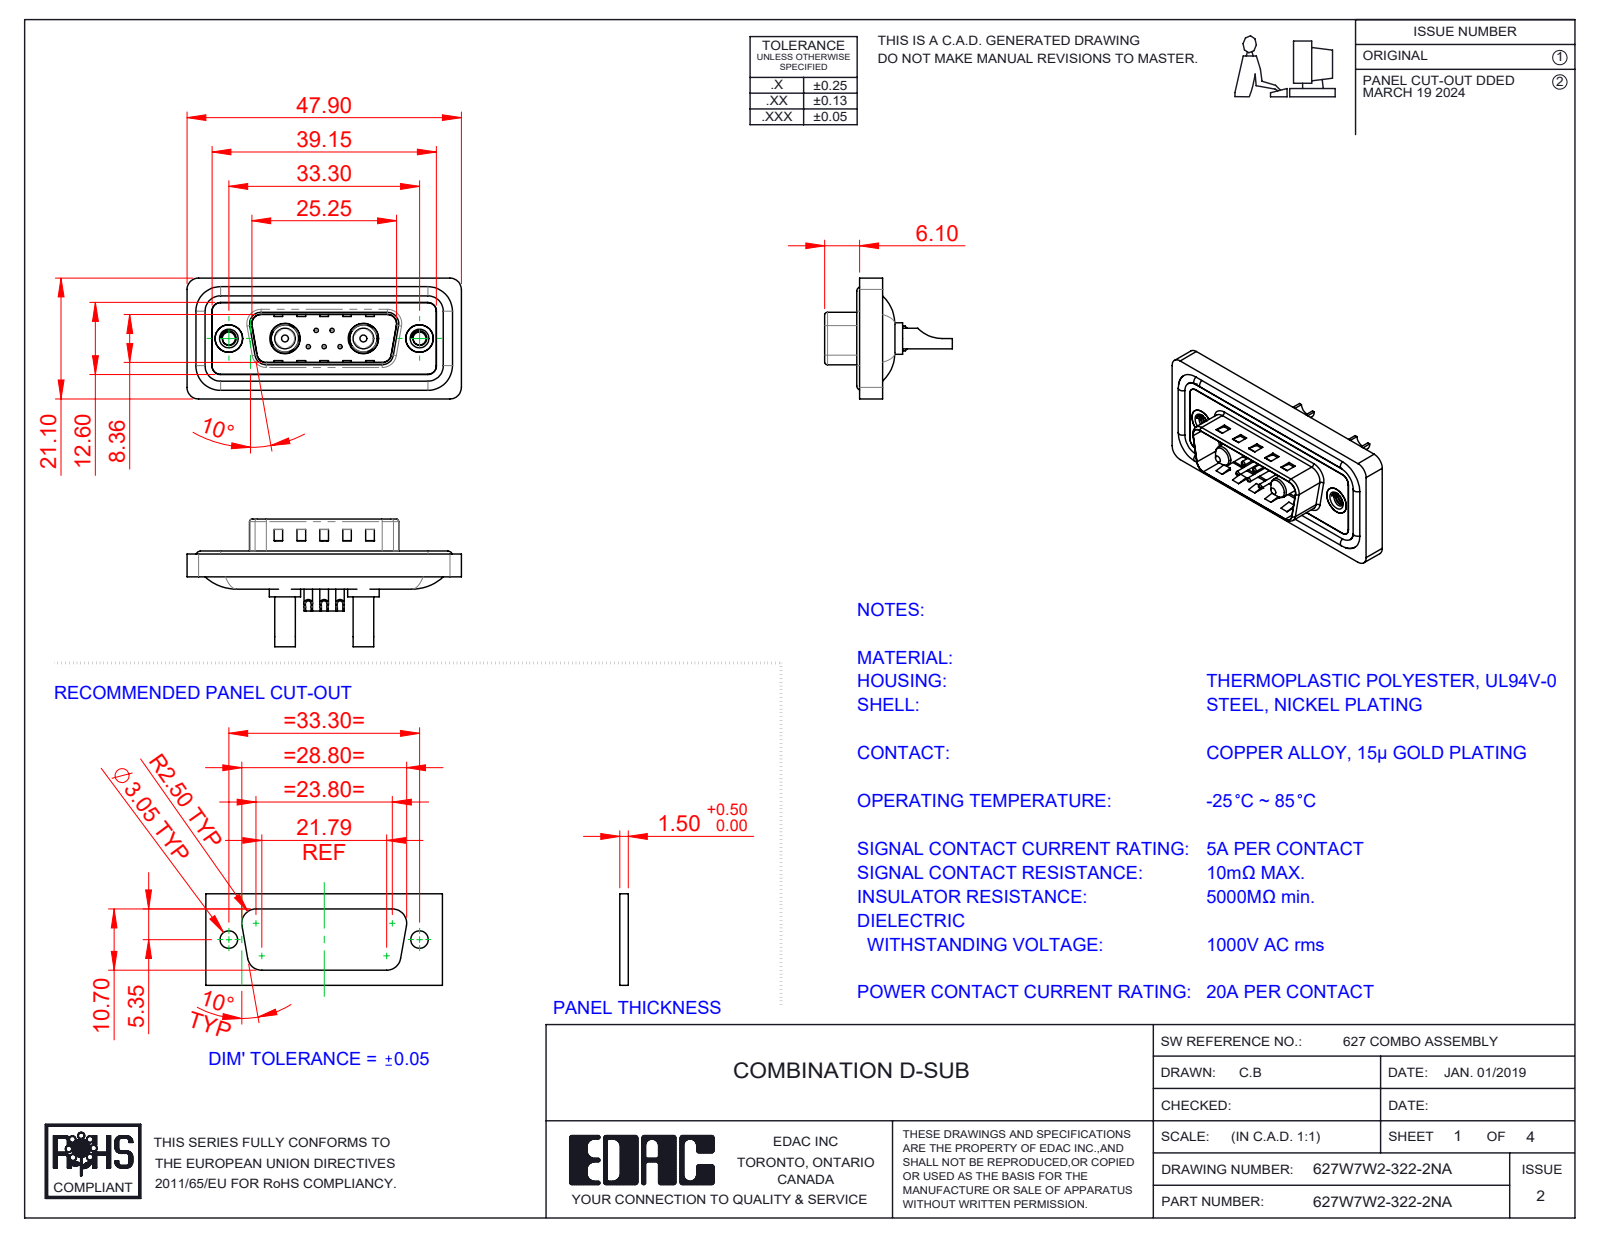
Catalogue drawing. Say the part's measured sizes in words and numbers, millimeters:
The part is named "627W7W2-322-2NA; 627Combo Contact Row 2_22; 627Combo Shell Rear_15 Contacts; 627Combo Threaded Rivet_A (+5 more)". Its 3-D file was written by "SolidWorks 2023 (CONFIG_CONTROL_DESIGN)". It is 16 solids with 722 faces: 248 planar, 310 cylindrical and 164 other. Overall it measures 47.9 by 22.3 by 21.1 millimeters. Its volume is 5 552 cubic millimeters and its surface area 8 995 square millimeters. Round holes: 5 of diameter 0.75, 5 of diameter 1, 5 of diameter 1.6, 5 of diameter 2, 2 of diameter 2.26, 2 of diameter 2.7, 2 of diameter 4, 2 of diameter 4.8, 2 of diameter 4.85, 2 of diameter 5, 2 of diameter 5.3. Round bosses or shafts: 5 of diameter 1.5, 4 of diameter 1.6, 2 of diameter 5.5, 2 of diameter 5.2, 2 of diameter 4.9, 2 of diameter 4.75, 2 of diameter 3.75, 2 of diameter 3.6. Partial cylindrical surfaces (rounded edges, fillets, slot ends): 26 of radius 1.5, 20 of radius 2, 8 of radius 0.5, 8 of radius 1.6, 6 of radius 1, 4 of radius 0.25, 4 of radius 0.6, 4 of radius 0.65. The main face-to-face distances are 0.4, 1.1, 1.6, 1.5, 0.5, 3.1, 2.9, 0.82, 9.58, 2.5. The hole center spacings are 3.16, 2.77, 9.8, 23.5, 4.31, 4.33, 5.03, 5.04.
